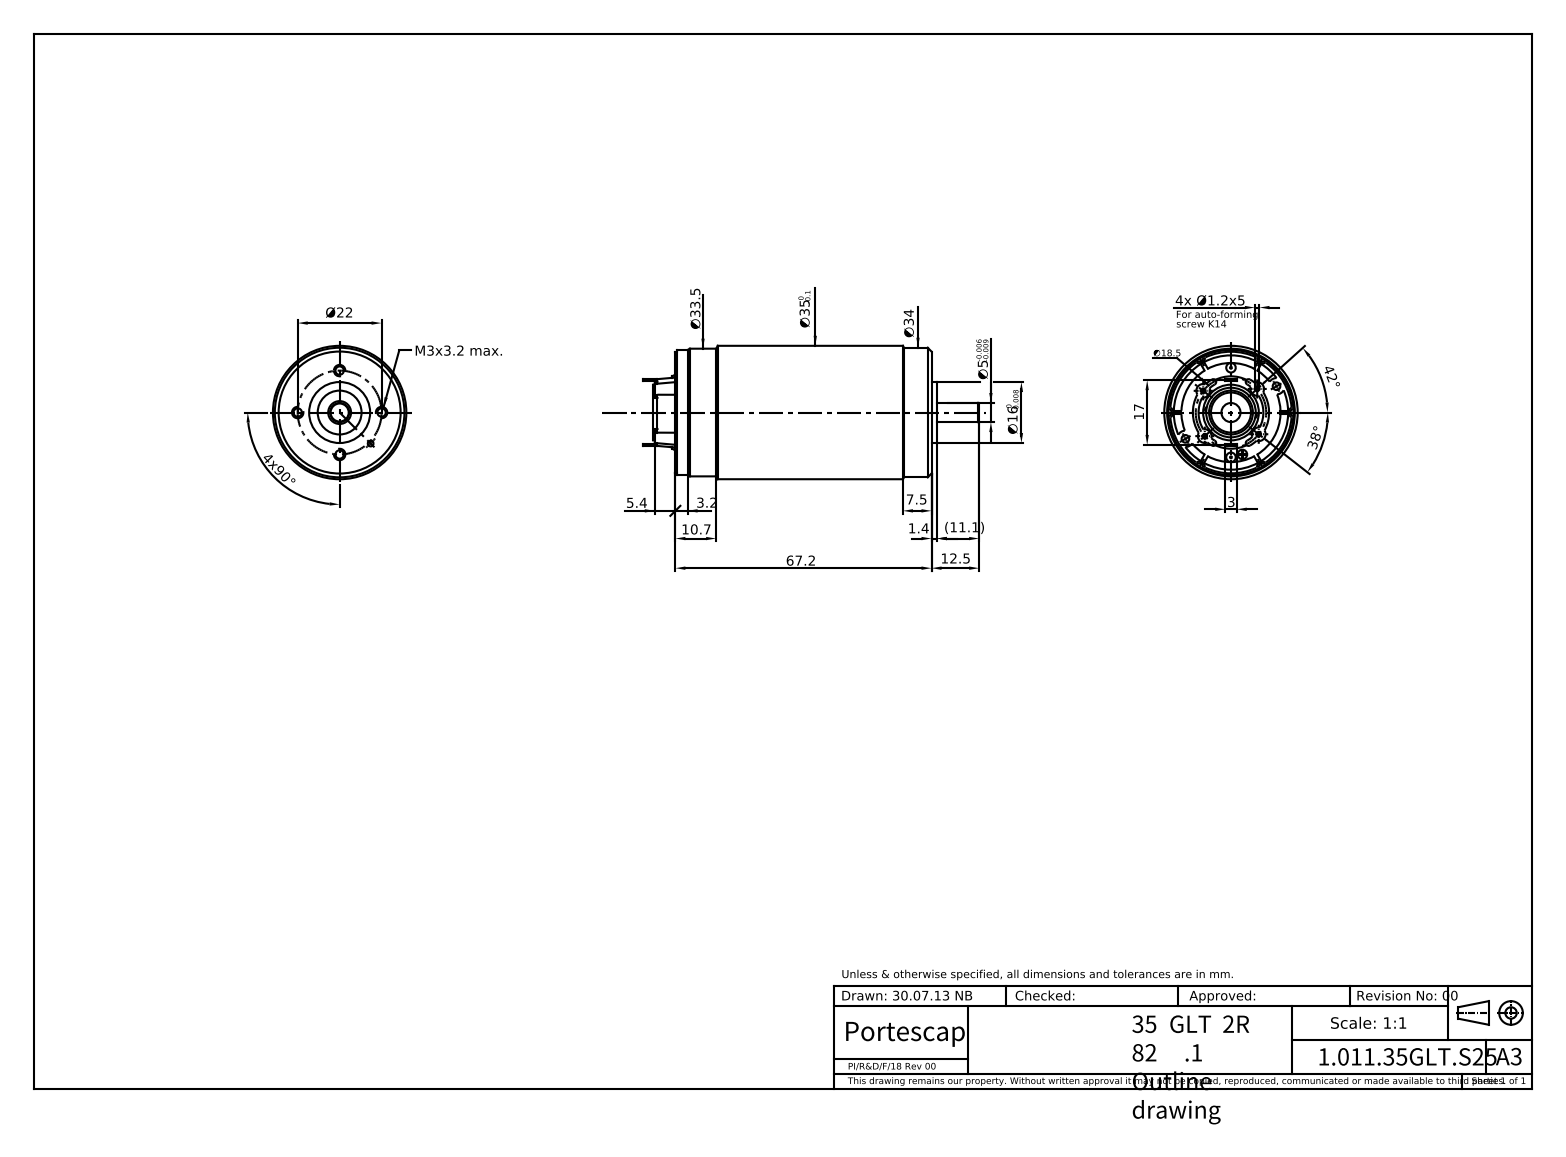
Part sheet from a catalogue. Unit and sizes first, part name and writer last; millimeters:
Units: millimetres
Overall size (bounding box): 86.07 × 35 × 35
Round holes (diameter × count): ⌀1.6 ×6, ⌀2.5 ×5, ⌀1 ×4, ⌀1.2 ×4, ⌀3 ×4, ⌀2 ×3, ⌀5 ×1, ⌀13 ×1
Round bosses / shafts (diameter × count): ⌀35 ×1, ⌀34 ×1, ⌀33.5 ×1, ⌀32.8 ×1, ⌀31.8 ×1, ⌀16 ×1
Partial cylindrical surfaces — rounded edges, fillets, slot ends (radius × count): R2.1 ×6, R0.2 ×4, R10 ×4, R2.15 ×2, R0.6 ×1
Main face-to-face distances: 0.5, 67.2, 66.7, 1.4, 68.1, 68.6, 69.56, 68.16, 1.46, 0.96
Hole centre spacings: 9.25, 11, 15.56, 13.86, 18.51, 3.5, 5.05, 5.52
Volume: 64 445 mm³ · Surface area: 10 687 mm²
Bodies: 1 solid, 251 faces (86 planar, 97 cylindrical, 68 other)
Part name (STEP PRODUCT): 35GLT_2R_82_50
STEP written by: PRO/ENGINEER BY PARAMETRIC TECHNOLOGY CORPORATION, 2014310 (CONFIG_CONTROL_DESIGN)
